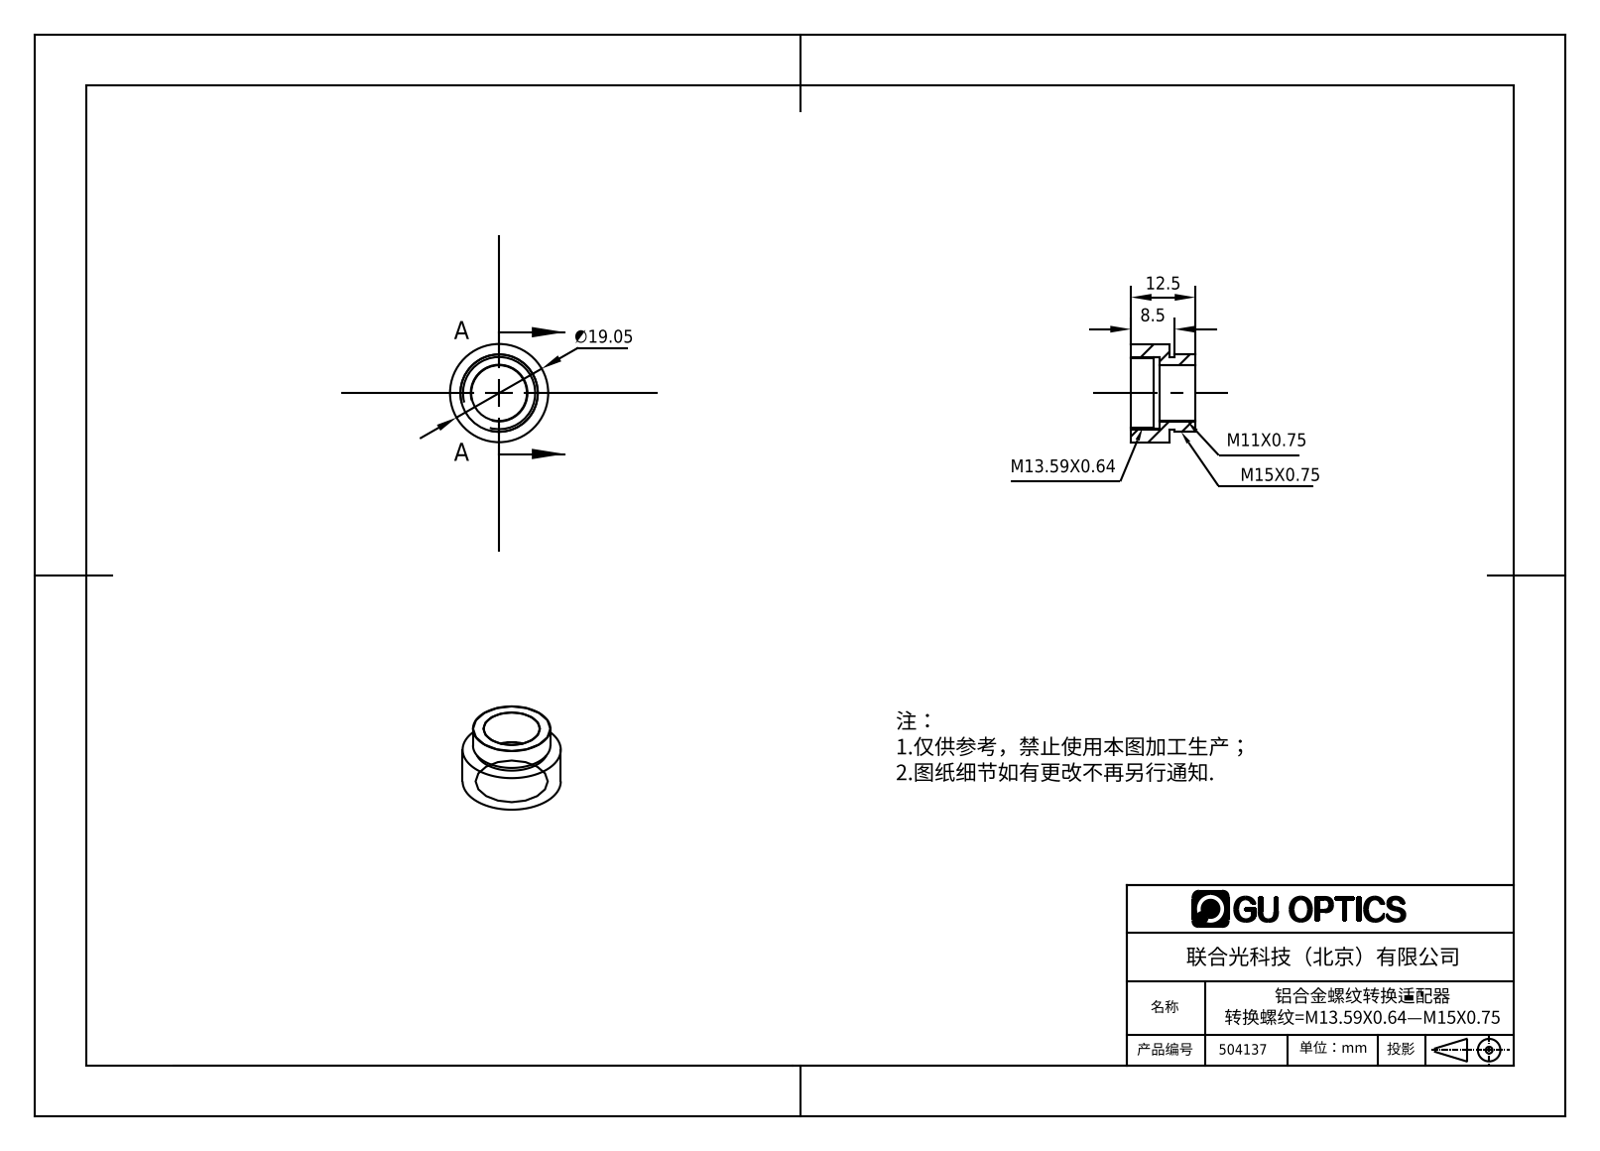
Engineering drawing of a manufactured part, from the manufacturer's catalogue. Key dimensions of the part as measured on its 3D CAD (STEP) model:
Part name (STEP PRODUCT): 504137
STEP written by: SolidWorks 2016 (AUTOMOTIVE_DESIGN)
Units: millimetres
Bodies: 1 solid, 18 faces (6 planar, 12 cylindrical, 0 other)
Overall size (bounding box): 19.05 × 19.05 × 12.5
Volume: 1 557 mm³ · Surface area: 1 597 mm²
Round holes (diameter × count): ⌀10.8 ×1, ⌀13.59 ×1, ⌀13.8 ×1
Round bosses / shafts (diameter × count): ⌀19.05 ×1, ⌀15.02 ×1, ⌀14 ×1
Main face-to-face distances: 7.5, 12.5, 5, 5.5, 2, 7, 1, 3, 4, 8.5
